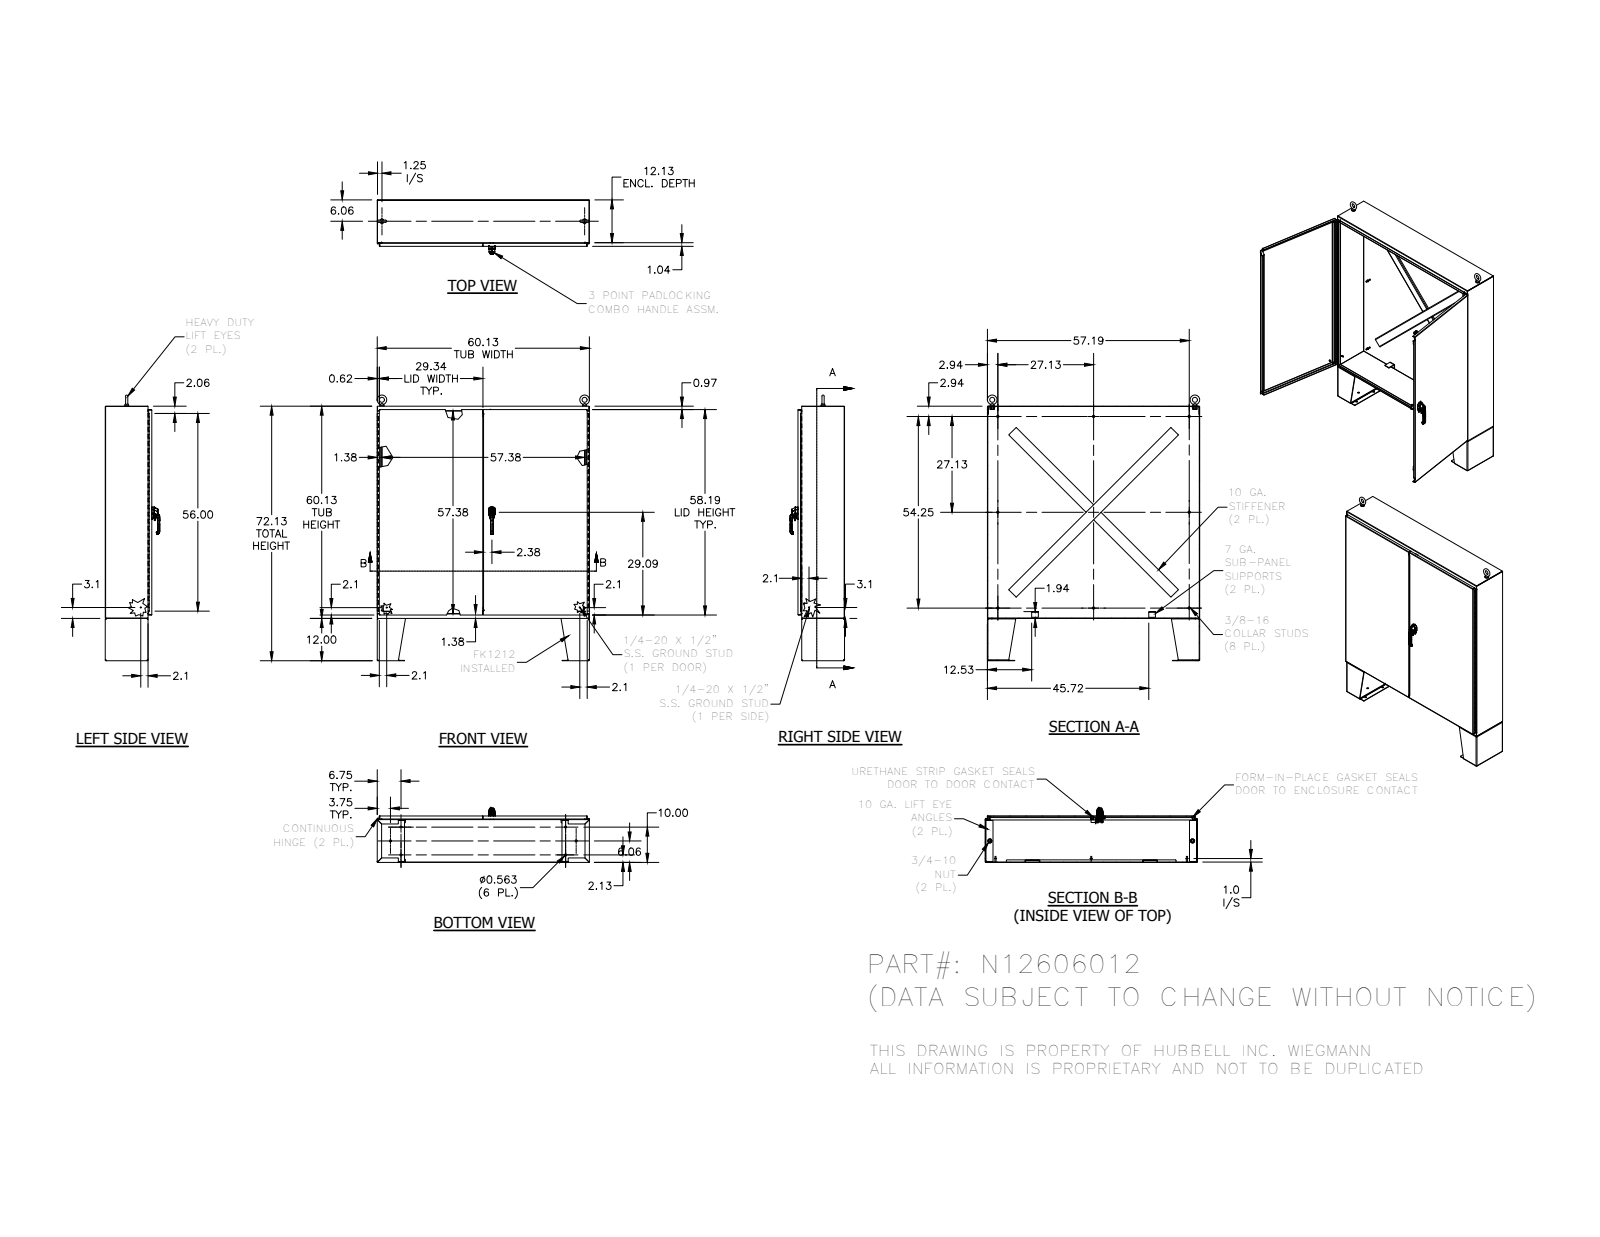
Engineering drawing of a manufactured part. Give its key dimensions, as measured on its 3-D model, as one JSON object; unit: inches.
{"part_name": "N12606012", "step_written_by": "SolidWorks 2018 (AUTOMOTIVE_DESIGN)", "units": "inches", "bodies": {"solids": 76, "faces": 2392, "planar": 1384, "cylindrical": 708, "other": 300}, "overall_size": [75.248, 61.293, 15.338], "volume_in3": 1305, "surface_area_in2": 26168, "round_holes": [[0.563, 18], [0.277, 8], [0.2, 4], [0.28, 3], [0.125, 2], [0.125, 2], [0.241, 2], [0.25, 2], [0.252, 2], [0.4, 2], [0.45, 2], [0.642, 2]], "round_bosses_or_shafts": [[0.33, 8], [0.625, 7], [0.25, 5], [0.337, 3], [1.25, 2], [1.12, 2], [1, 2], [0.75, 2]], "partial_cylinders_radius": [[0.031, 24], [0.094, 23], [0.219, 22], [0.05, 18], [0.025, 16], [0.125, 15], [0.03, 13], [0.067, 8]], "face_to_face_distances": [0.094, 13.067, 12.973, 13.16, 60.031, 60.125, 59.938, 0.125, 0.125, 12.031], "hole_center_spacings": [2.041, 4.95, 5, 6.688, 10.75, 11.856, 46.398, 49.667]}
